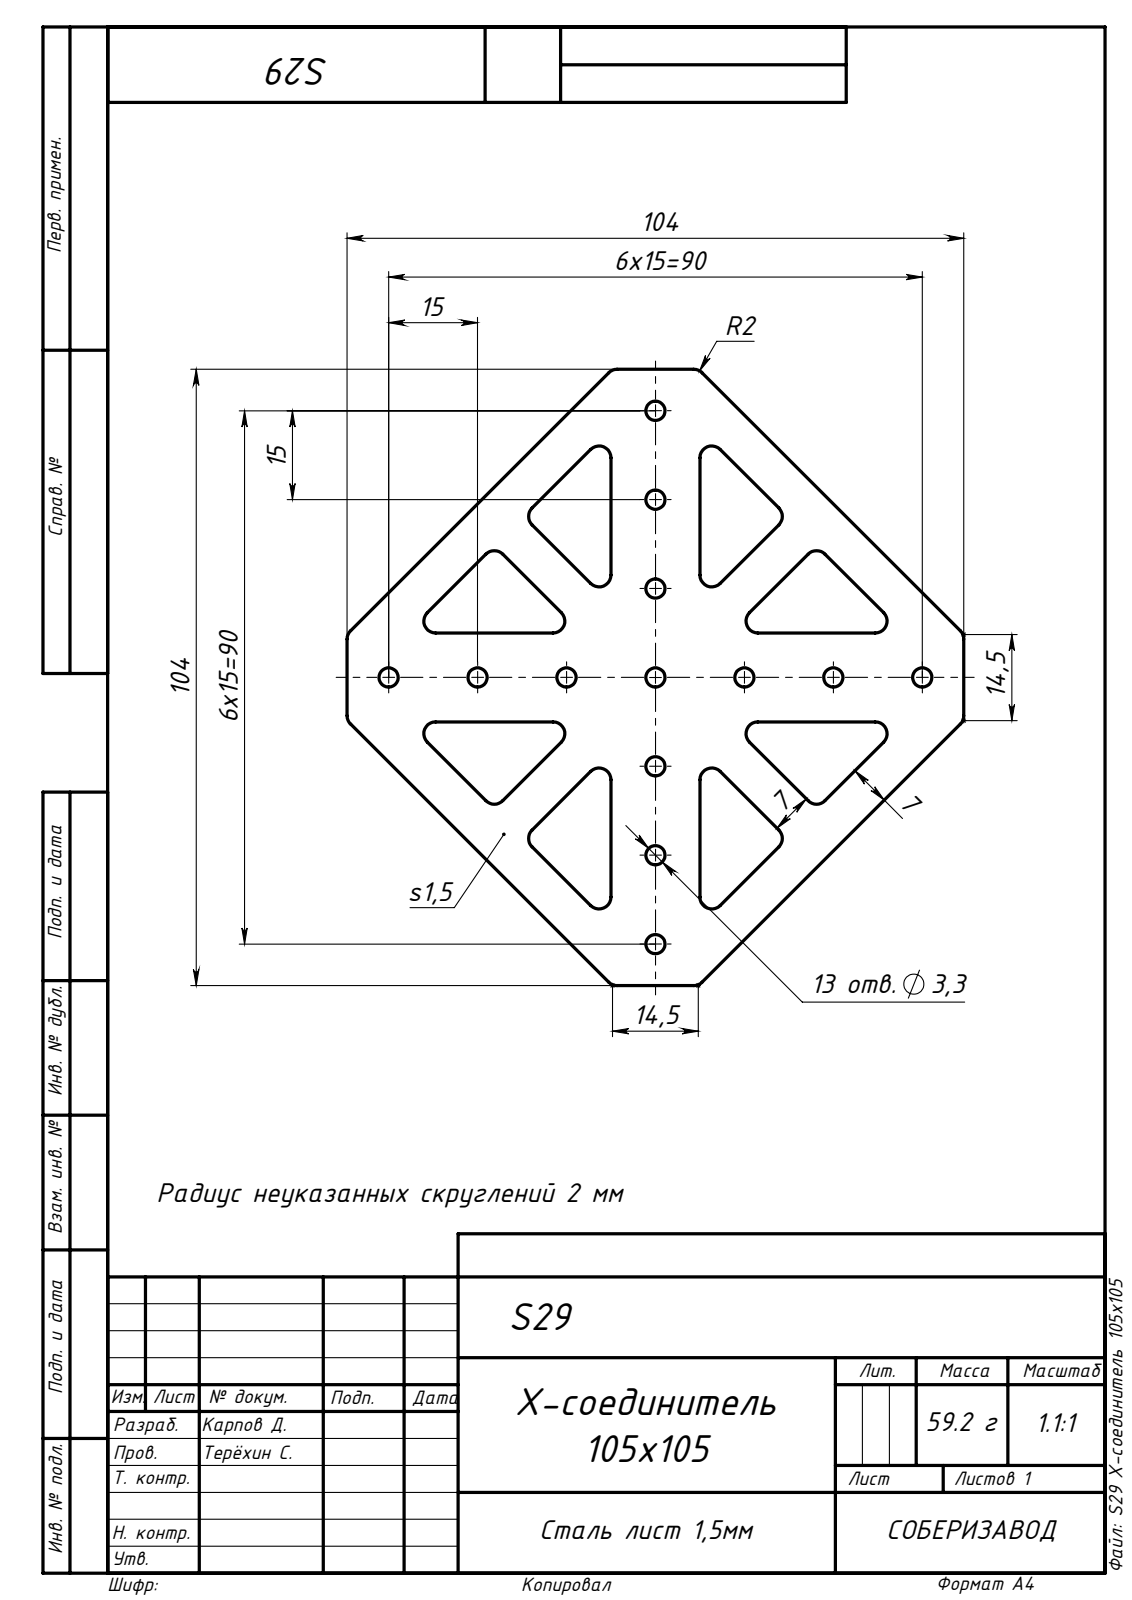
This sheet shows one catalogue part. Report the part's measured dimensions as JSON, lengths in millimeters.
{"step_written_by": "SolidWorks 2019 (AUTOMOTIVE_DESIGN)", "units": "millimeters", "bodies": {"solids": 1, "faces": 96, "planar": 34, "cylindrical": 62, "other": 0}, "overall_size": [104, 104, 1.5], "volume_mm3": 7593, "surface_area_mm2": 11513, "round_holes": [[3.25, 13]], "partial_cylinders_radius": [[2, 32]], "face_to_face_distances": [1.5, 38.42, 7, 83.84, 45.42, 76.84, 31.42, 15, 69.84, 44.5], "hole_center_spacings": [15, 30, 33.54, 45, 47.43, 54.08, 60, 21.21]}
